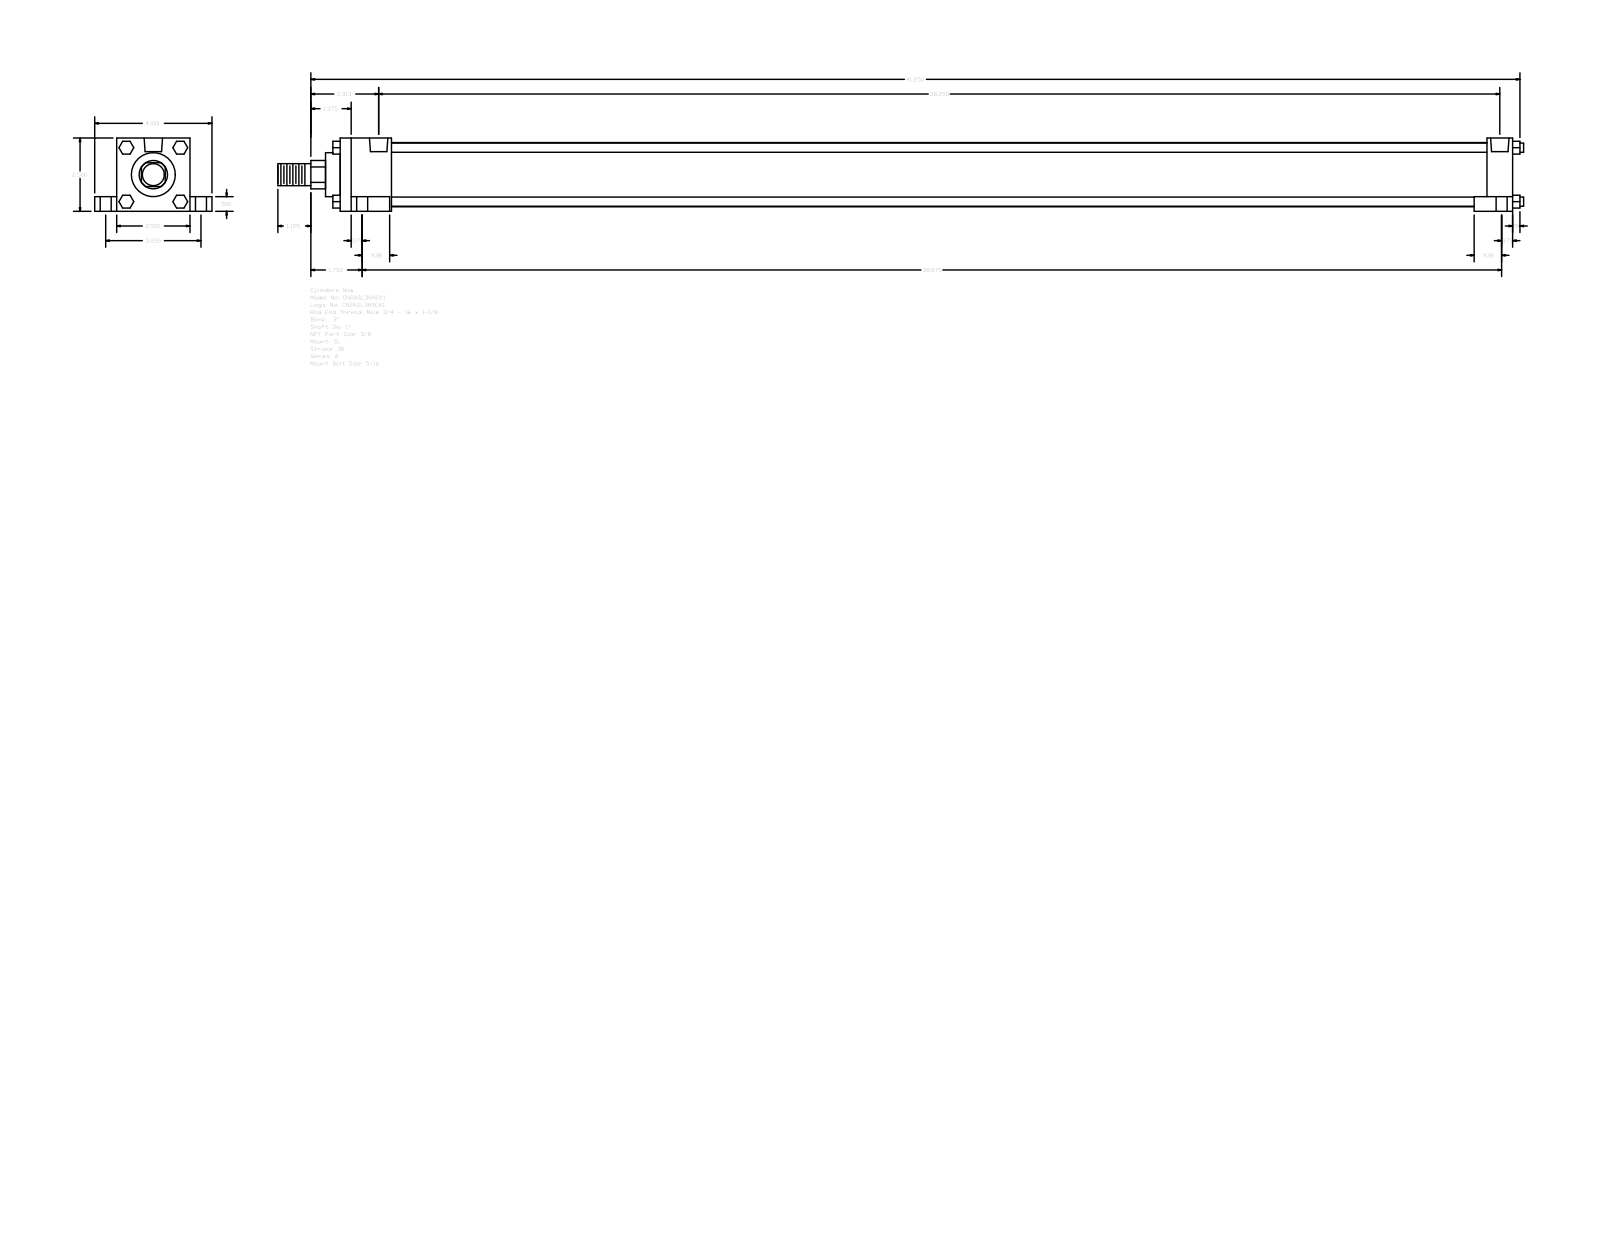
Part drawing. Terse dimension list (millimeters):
name: A_SL__0200_1
written by: GSSL Pune (CONFIG_CONTROL_DESIGN)
unit: mm
bodies: 0 solids, 148 faces (112 planar, 36 cylindrical, 0 other)
size: 1079.5 × 101.6 × 63.5
holes: 4× ⌀5.56, 4× ⌀9.53, 4× ⌀15.88, 2× ⌀15.93
bosses: 4× ⌀7.94, 1× ⌀55.63, 1× ⌀38.1, 1× ⌀25.4, 1× ⌀19.05
rounds: 1× R12.29
face distances: 63.5, 1016, 12.7, 50.8, 19.05, 82.55, 44.45, 971.55, 993.77, 949.32
hole spacings: 41.3, 41.64, 43.67, 44.22, 82.54, 965.98, 972.43, 974.01
